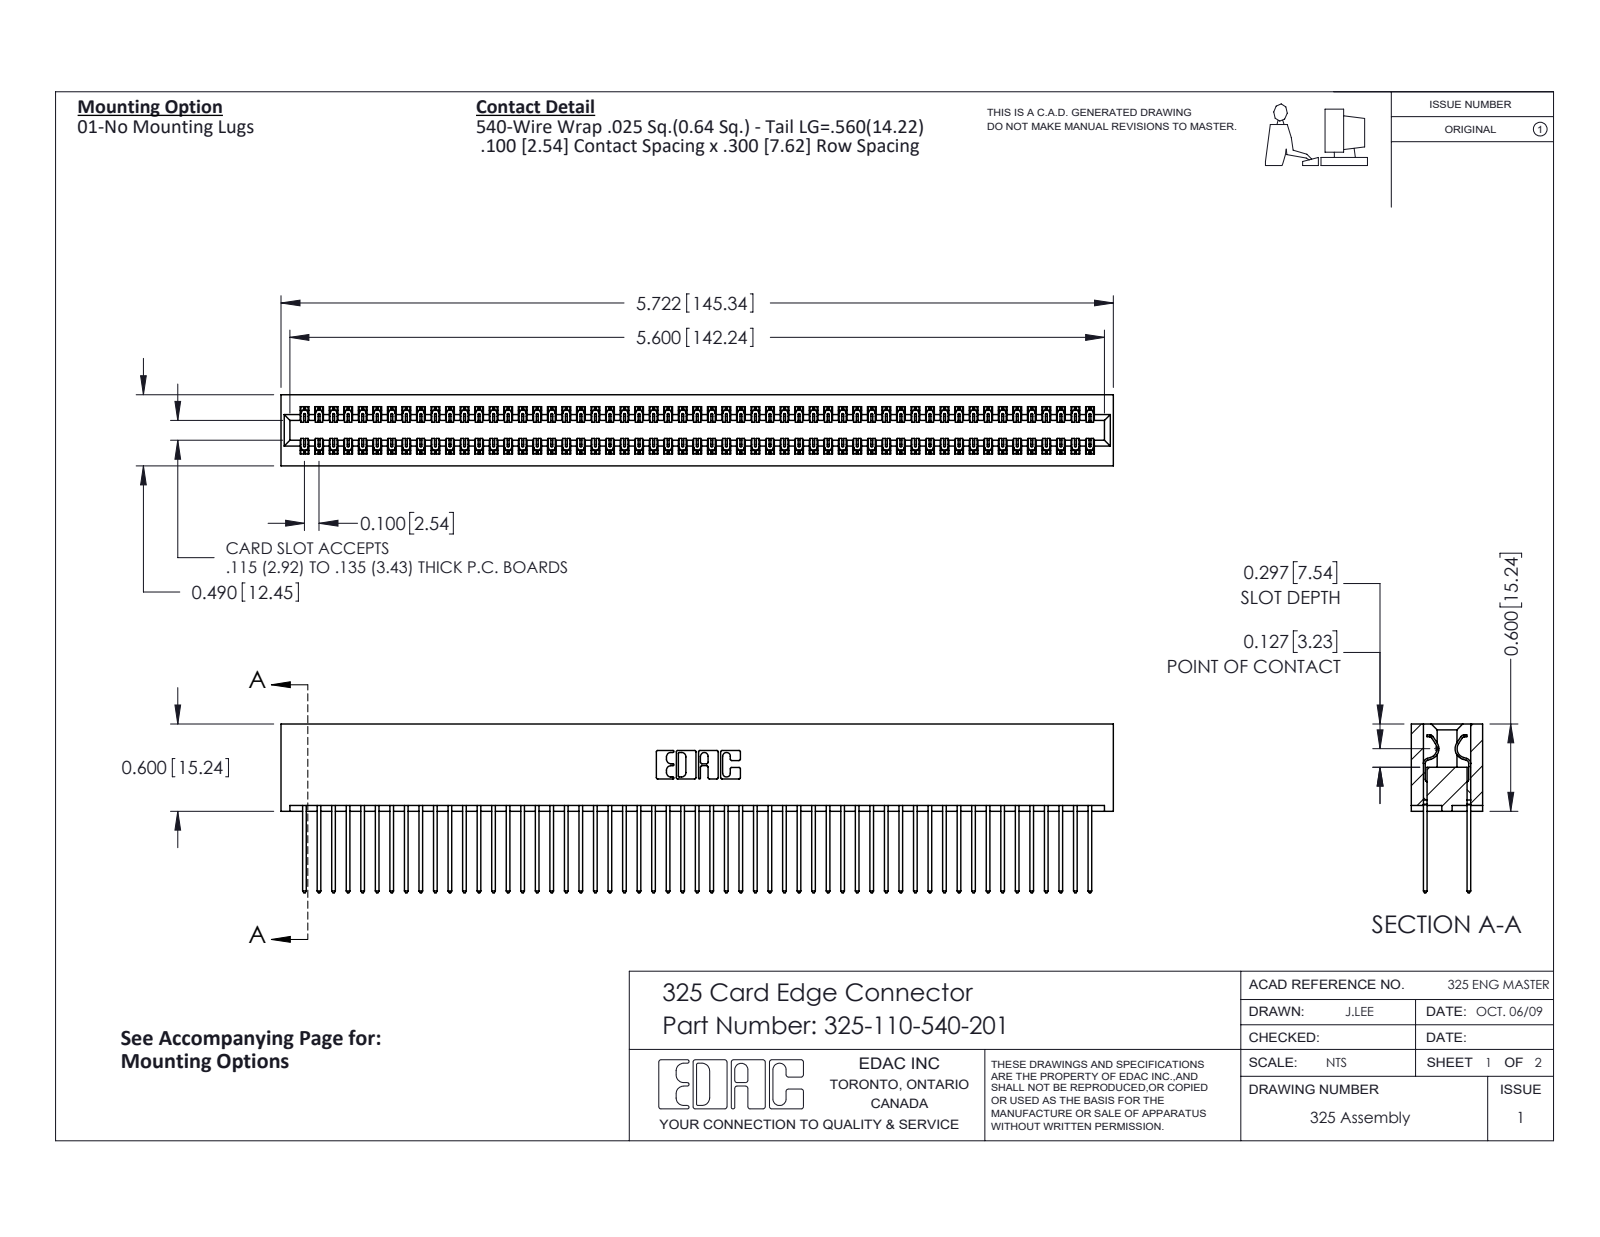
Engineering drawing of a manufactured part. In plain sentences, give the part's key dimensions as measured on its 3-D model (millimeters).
The part is named "325-110-540-201; 325 Part_Lugless; 325-292-001_325-293-140". Its 3-D file was written by "SolidWorks 2016 (CONFIG_CONTROL_DESIGN)". It is 111 solids with 5826 faces: 4026 planar, 1800 cylindrical and 0 other. Overall it measures 145.3 by 29.5 by 12.4 millimeters. Its volume is 19 910 cubic millimeters and its surface area 27 050 square millimeters. Partial cylindrical surfaces (rounded edges, fillets, slot ends): 165 of radius 0.2, 110 of radius 0.3, 22 of radius 0.3, 6 of radius 0.2, 6 of radius 0.8, 3 of radius 0.7, 2 of radius 0.4, 2 of radius 0.6. The main face-to-face distances are 2.1, 10.3, 7.6, 2.7, 9.7, 0.6, 8.3, 12.4, 7, 14.2.
